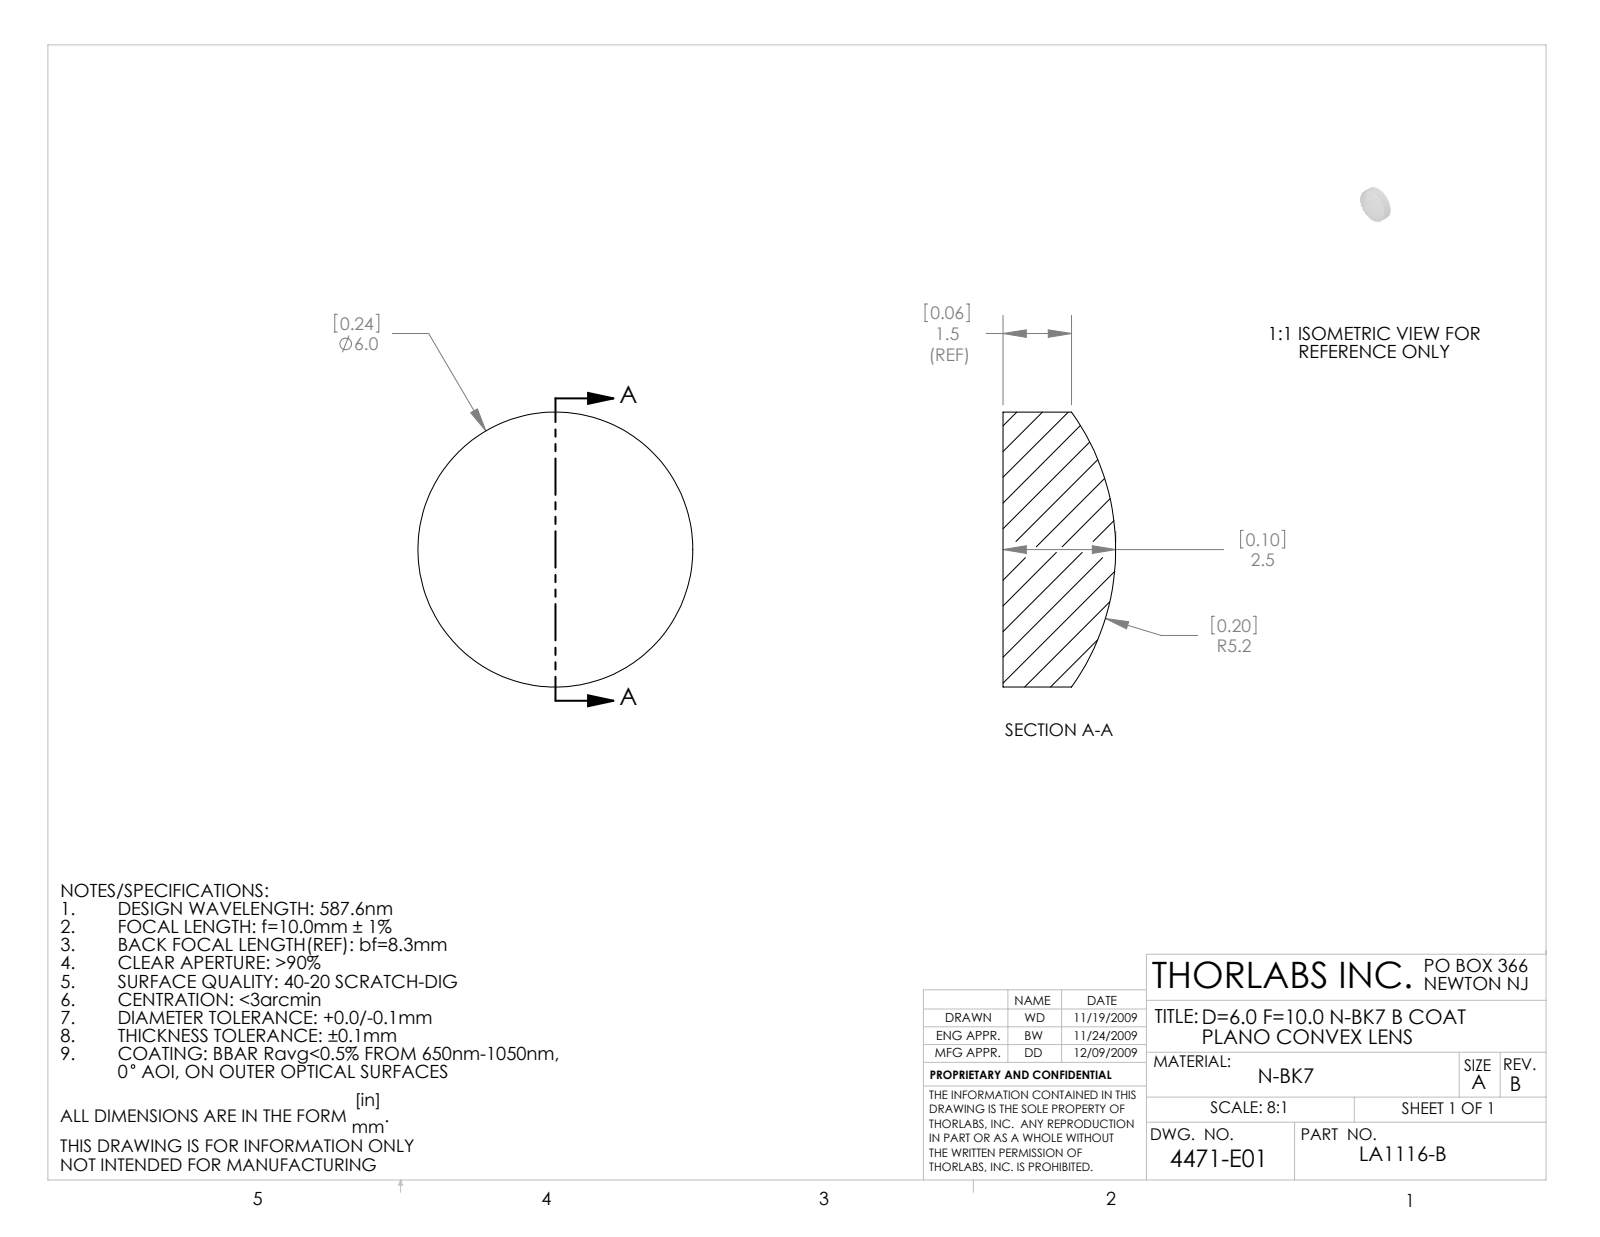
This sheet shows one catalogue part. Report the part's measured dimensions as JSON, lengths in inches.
{"part_name": "4471-E0W", "step_written_by": "SolidWorks 2009 (AUTOMOTIVE_DESIGN)", "units": "inches", "bodies": {"solids": 1, "faces": 5, "planar": 1, "cylindrical": 2, "other": 2}, "overall_size": [0.236, 0.236, 0.097], "volume_in3": 0.003, "surface_area_in2": 0.14, "round_bosses_or_shafts": [[0.236, 1]]}
